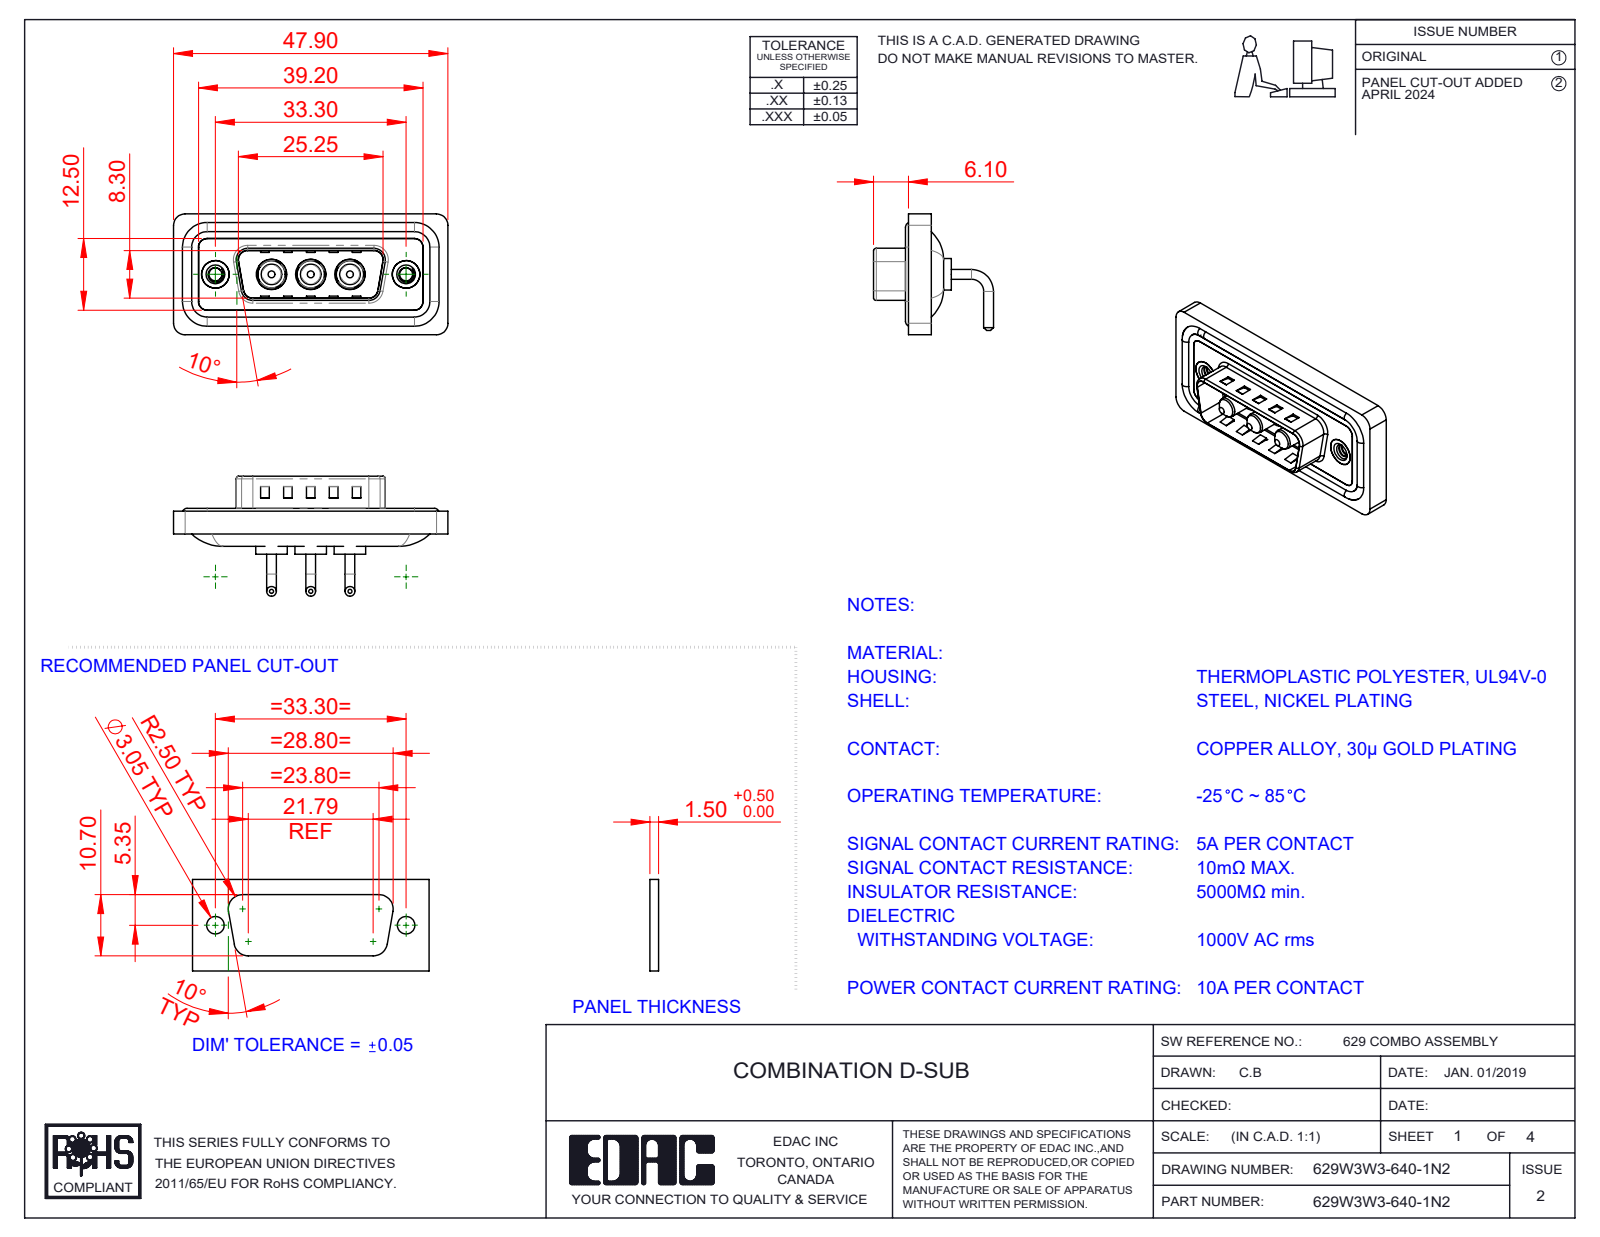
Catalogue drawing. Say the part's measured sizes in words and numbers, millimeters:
The part is named "629Combo Shell Rear_15 Contacts; Power Pin_10A RA; 629Combo Waterproof Housing_15 Contacts; 629Combo Shell Front_15 Contacts (+3 more)". Its 3-D file was written by "SolidWorks 2023 (CONFIG_CONTROL_DESIGN)". It is 13 solids with 576 faces: 207 planar, 247 cylindrical and 122 other. Overall it measures 47.9 by 21.1 by 20.95 millimeters. Its volume is 5 615 cubic millimeters and its surface area 8 884 square millimeters. Round holes: 3 of diameter 4.85, 3 of diameter 5.3, 2 of diameter 2.26, 2 of diameter 4, 2 of diameter 4.8, 2 of diameter 5. Round bosses or shafts: 6 of diameter 1.7, 4 of diameter 1.6, 3 of diameter 5.5, 3 of diameter 5.2, 3 of diameter 4.75, 3 of diameter 3.75, 3 of diameter 3.6, 2 of diameter 4.9. Partial cylindrical surfaces (rounded edges, fillets, slot ends): 20 of radius 2, 18 of radius 1.5, 8 of radius 0.5, 8 of radius 1.6, 4 of radius 0.25, 4 of radius 0.6, 4 of radius 0.65, 4 of radius 0.9. The main face-to-face distances are 0.4, 2.9, 0.8, 1.1, 2.1, 1.6, 3.1, 2.5, 4.5, 1.5. The hole center spacings are 6.85, 9.8, 16.65, 23.5, 13.7, 33.3.
